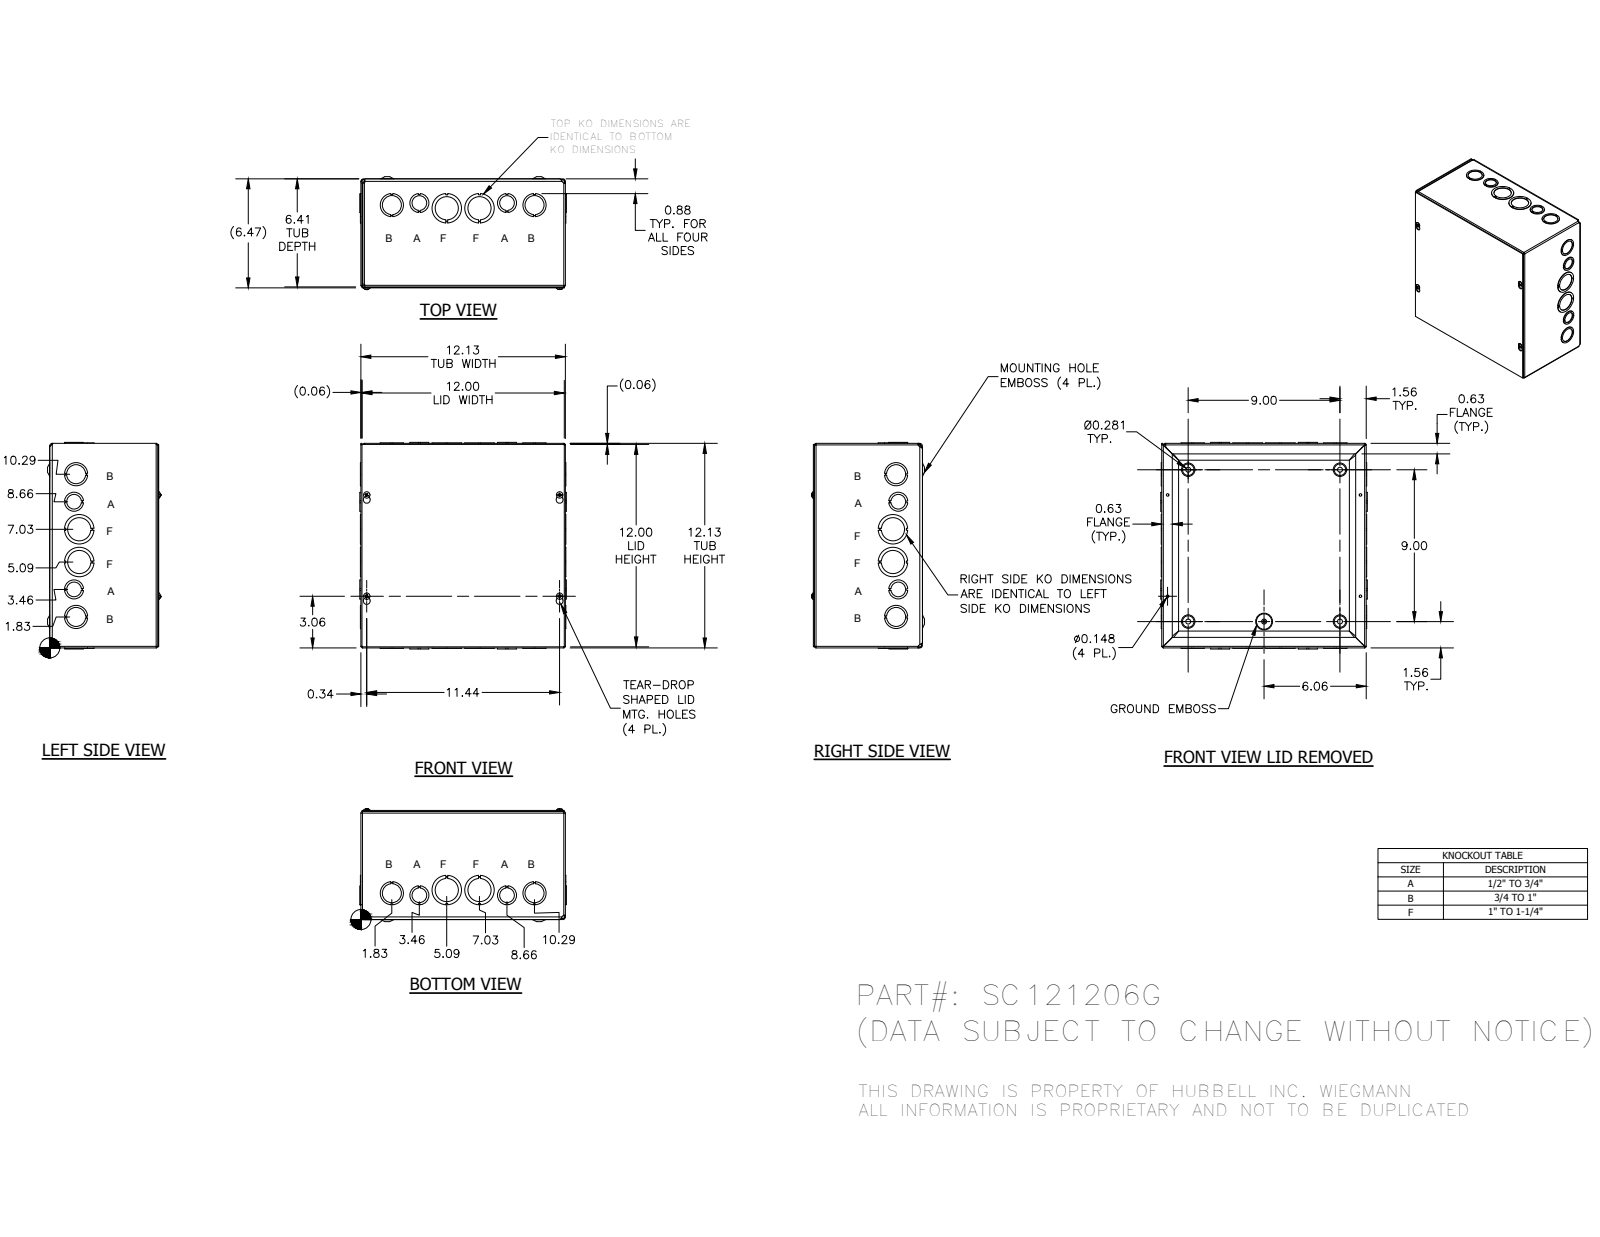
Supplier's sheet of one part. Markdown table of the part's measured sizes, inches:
| quantity | value |
| --- | --- |
| part name | SC1212GBKP; SC121206GWRA; SC1212GLID; 34056 (+1 more) |
| STEP written by | Autodesk Inventor 2014 (AUTOMOTIVE_DESIGN) |
| units | inches |
| bodies | 22 solids, 1030 faces (662 planar, 217 cylindrical, 151 other) |
| overall size | 12.249 × 12.249 × 6.693 |
| round holes (diameter × count) | 1.125 × 8, 1.375 × 8, 0.148 × 4, 0.3 × 4, 0.875 × 4, 1.75 × 4, 0.165 × 1 |
| round bosses / shafts (diameter × count) | 0.384 × 4, 0.164 × 4, 0.228 × 1 |
| partial cylindrical surfaces (radius × count) | 0.031 × 8, 0.093 × 8, 0.055 × 4, 0.062 × 4, 0.094 × 4, 0.11 × 4, 0.117 × 4, 0.124 × 4 |
| main face-to-face distances | 0.062, 12.063, 6.343, 12.125, 6.405, 12.001, 0.063, 6.406, 6.468, 0.062 |
| hole center spacings | 1.635, 1.659, 1.933, 3.265, 3.584, 5.204, 6.831, 7.598 |
